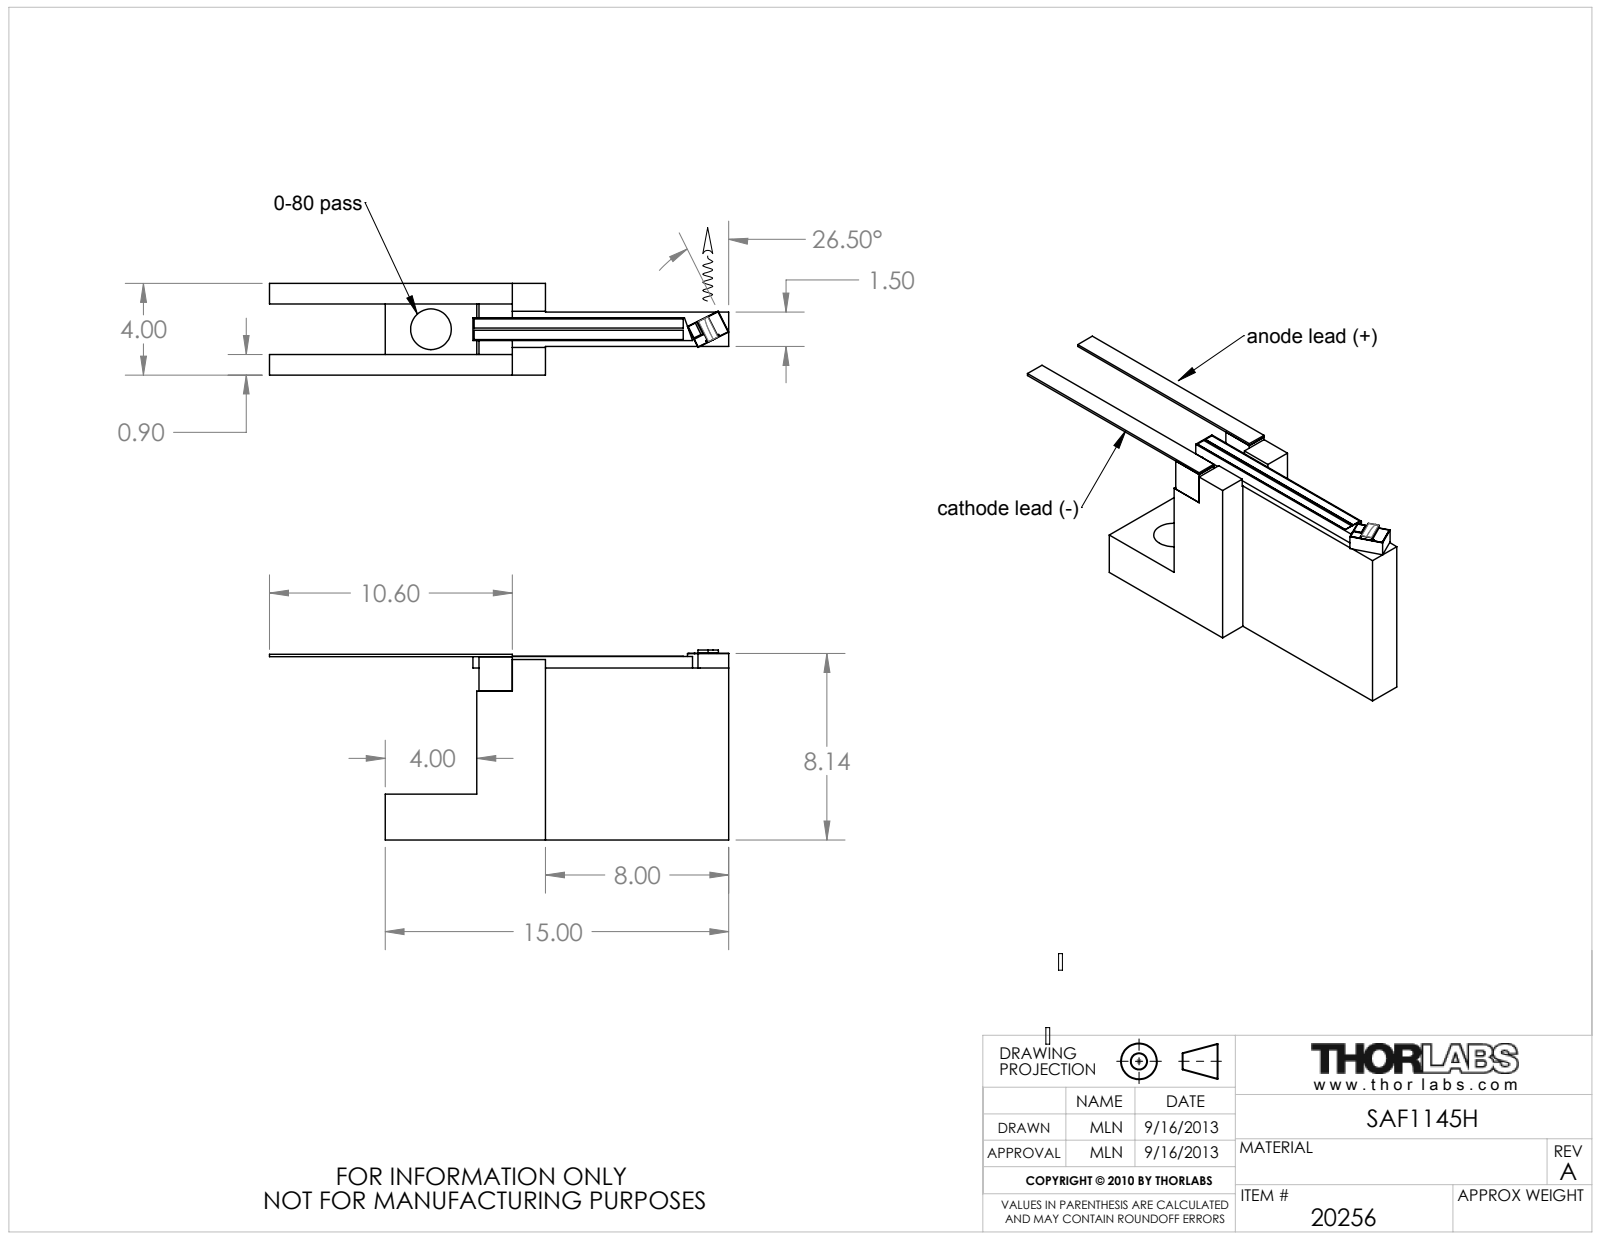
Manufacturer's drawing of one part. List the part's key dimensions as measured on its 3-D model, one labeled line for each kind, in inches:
Part name (STEP PRODUCT): 20256-E0W
STEP written by: SolidWorks 2012 (AUTOMOTIVE_DESIGN)
Units: inches
Bodies: 0 solids, 80 faces (78 planar, 2 cylindrical, 0 other)
Overall size (bounding box): 0.789 × 0.326 × 0.157
Round holes (diameter × count): ⌀0.07 ×1
Main face-to-face distances: 0.059, 0.049, 0.108, 0.157, 0.315, 0.024, 0.295, 0.02, 0.319, 0.118
